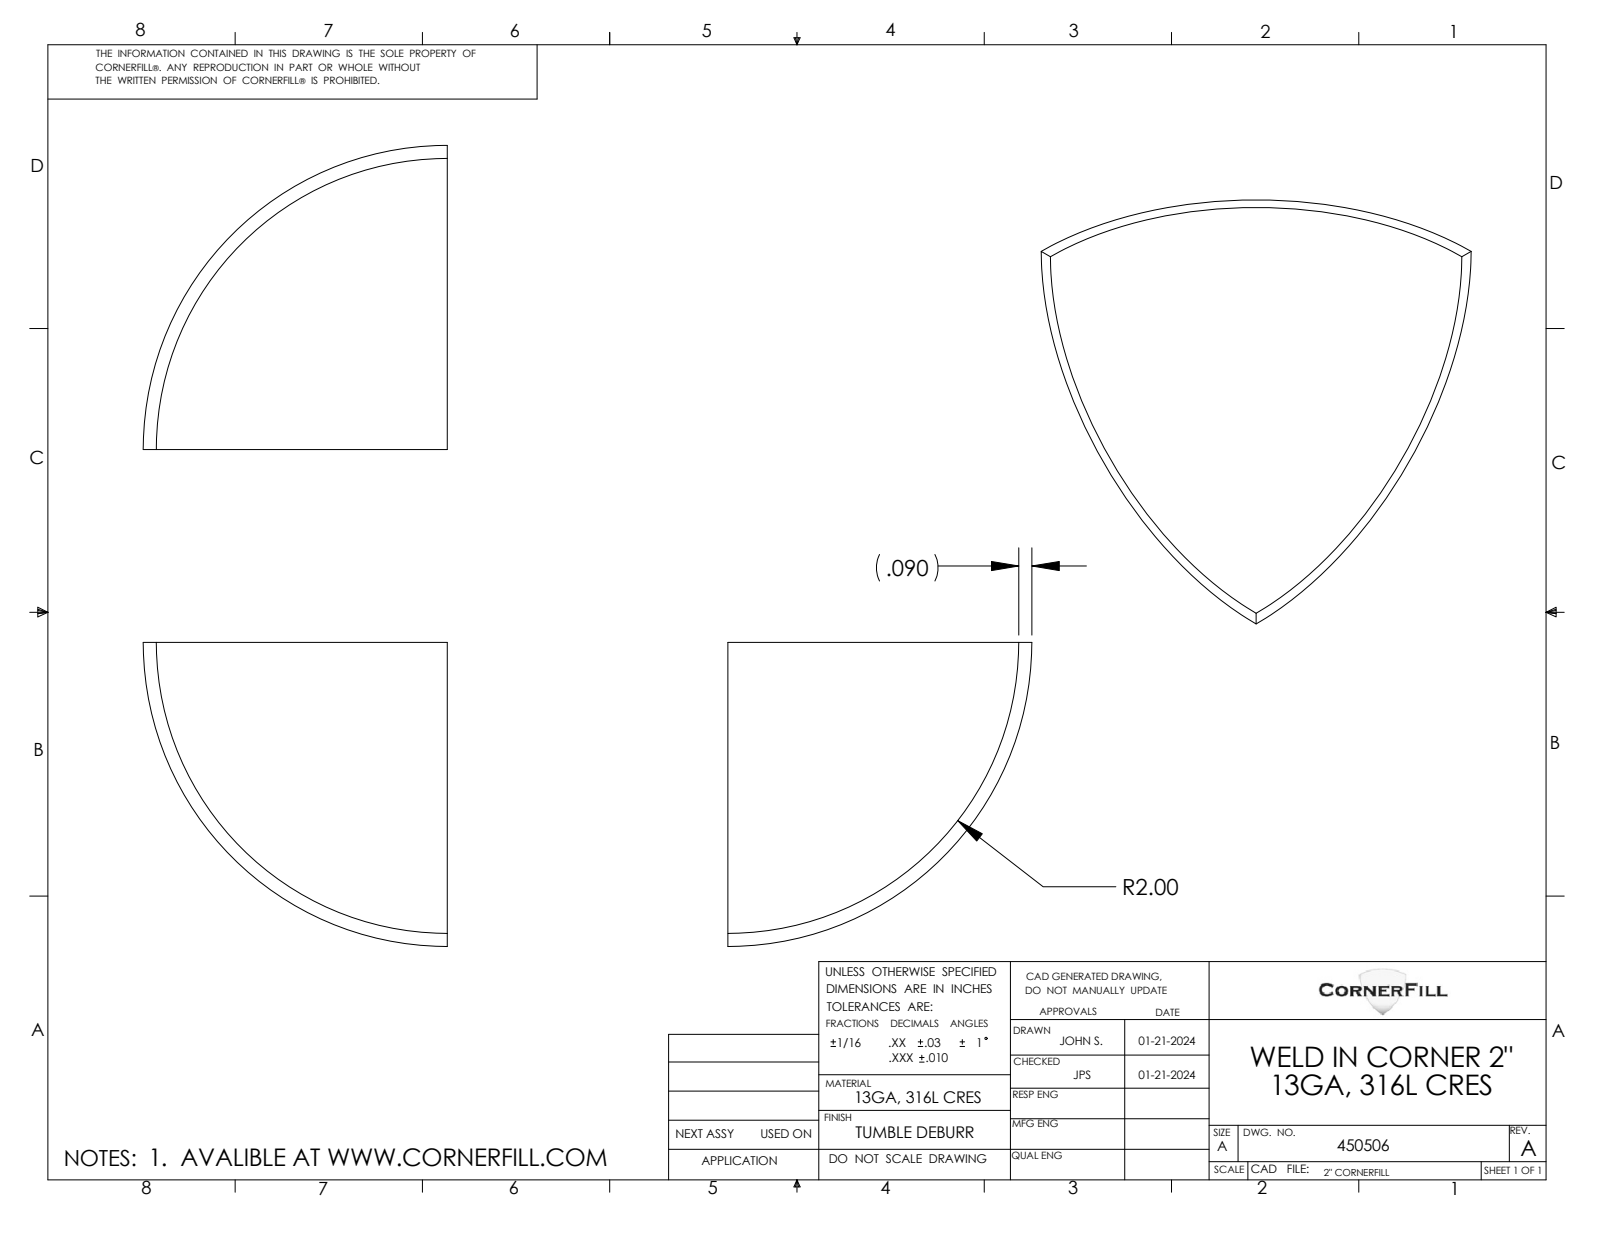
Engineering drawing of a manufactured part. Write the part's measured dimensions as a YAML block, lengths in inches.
part_name: "450506"
step_written_by: "SolidWorks 2021 (CONFIG_CONTROL_DESIGN)"
units: inches
bodies: {solids: 1, faces: 5, planar: 3, cylindrical: 0, other: 2}
overall_size: [2.956, 2.09, 2.09]
volume: 0.591
surface_area: 14.01
